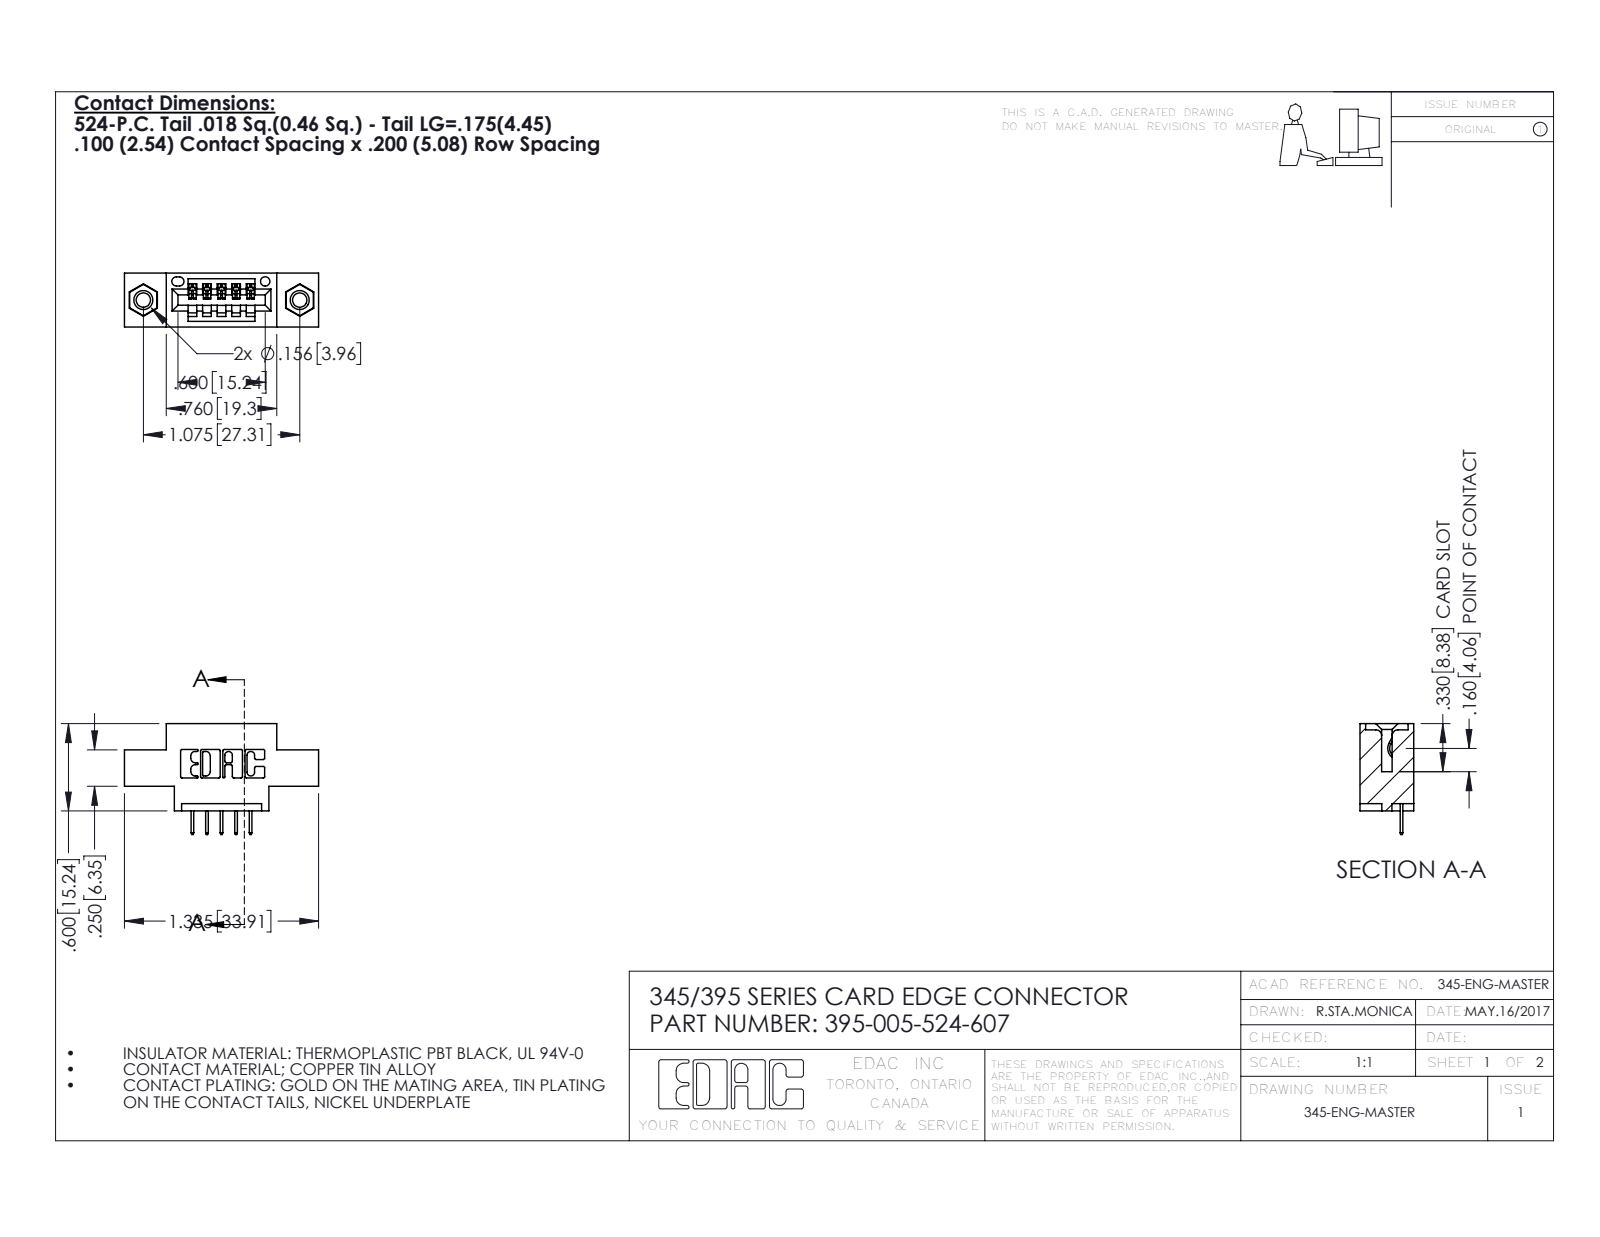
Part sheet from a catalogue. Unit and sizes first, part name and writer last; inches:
Units: inches
Overall size (bounding box): 1.335 × 0.762 × 0.37
Round holes (diameter × count): ⌀0.098 ×2, ⌀0.125 ×2, ⌀0.156 ×2, ⌀0.064 ×1
Round bosses / shafts (diameter × count): ⌀0.155 ×2
Partial cylindrical surfaces — rounded edges, fillets, slot ends (radius × count): R0.01 ×22, R0.006 ×10, R0.007 ×6, R0.031 ×6, R0.026 ×3, R0.031 ×2, R0.04 ×2, R0.014 ×1
Main face-to-face distances: 0.37, 0.2, 0.1, 0.072, 0.298, 0.025, 0.25, 0.06, 0.55, 0.15
Hole centre spacings: 0.27, 0.847, 1.075
Volume: 0.169 in³ · Surface area: 5.077 in²
Bodies: 8 solids, 500 faces (346 planar, 138 cylindrical, 16 other)
Part name (STEP PRODUCT): 345-250-001_345-250-005-103; 345-292-001_345-293-124; 345 Part_0.170 Offset - 0.156 Dia-TI; 395-005-524-607
STEP written by: SolidWorks 2016 (CONFIG_CONTROL_DESIGN)
